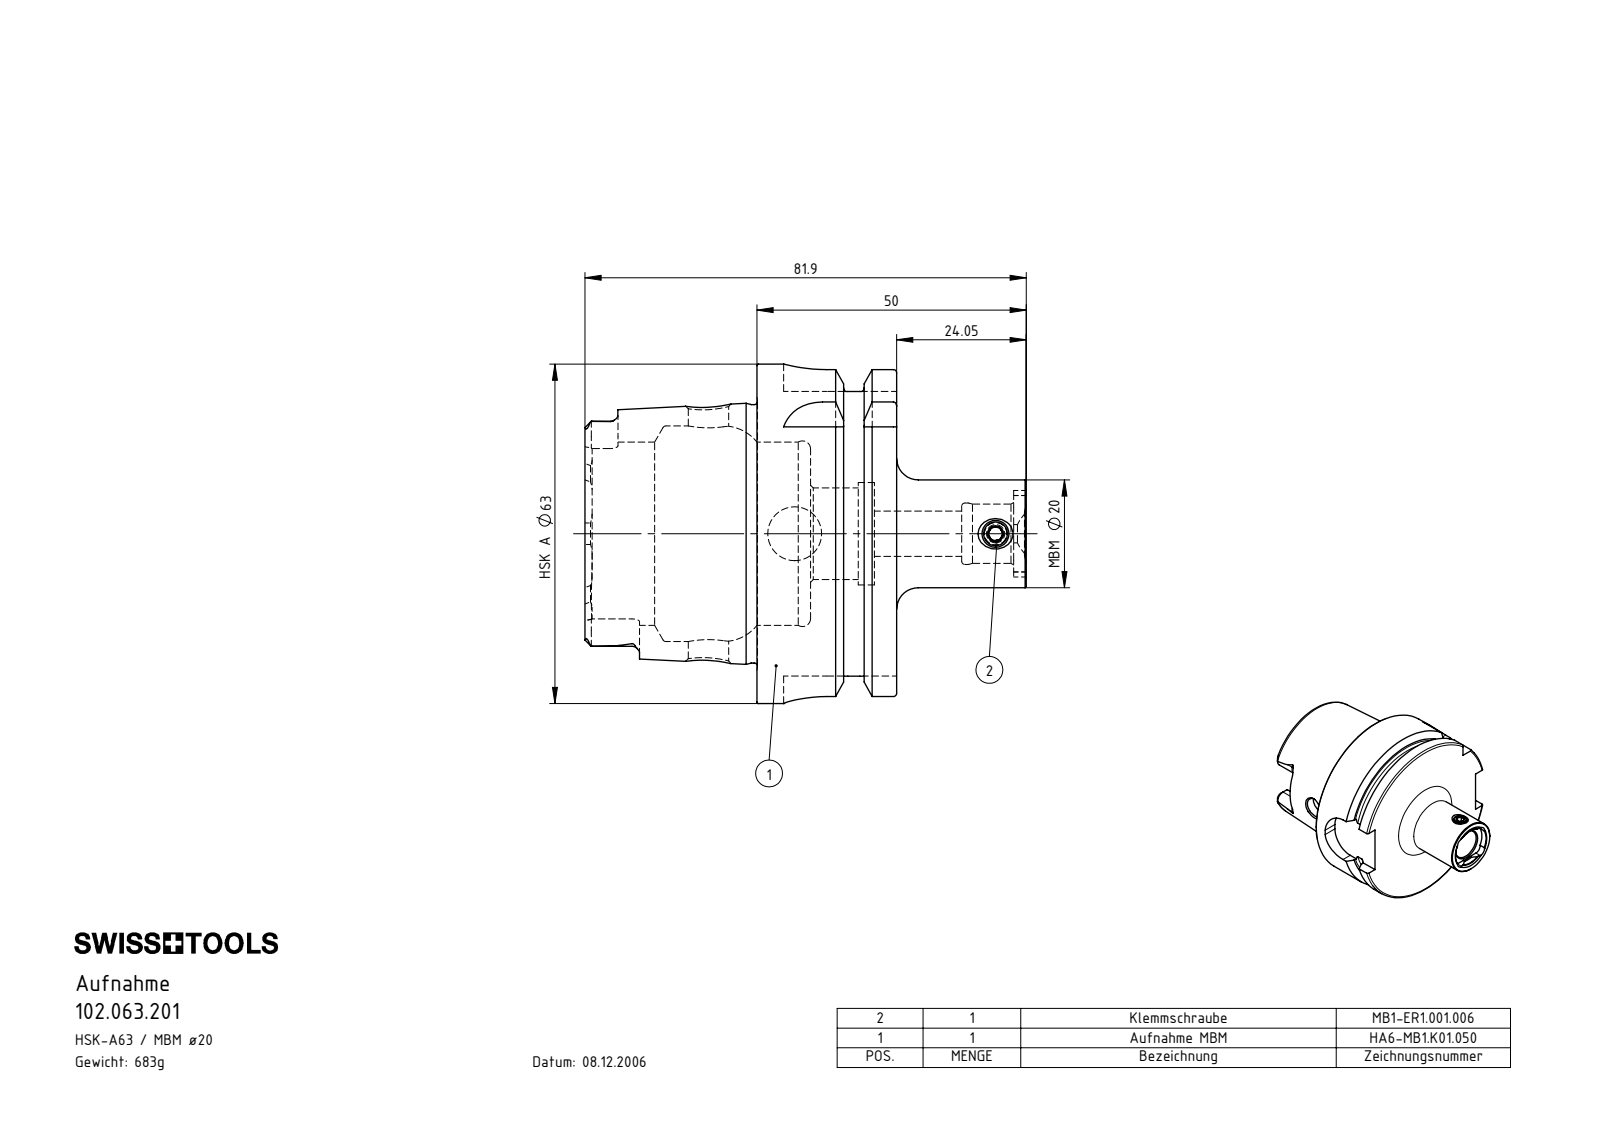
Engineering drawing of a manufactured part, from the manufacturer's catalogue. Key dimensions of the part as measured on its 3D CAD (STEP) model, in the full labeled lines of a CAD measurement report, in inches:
Part name (STEP PRODUCT): HA6.MB1.K01.050; HA6-MB1.K01.050_A_Fertigbearbeitung; MB1-ER1.001.006_A
STEP written by: SolidWorks 2012 (CONFIG_CONTROL_DESIGN)
Units: inches
Bodies: 2 solids, 228 faces (62 planar, 64 cylindrical, 102 other)
Overall size (bounding box): 3.224 × 2.48 × 2.48
Volume: 5.309 in³ · Surface area: 38.03 in²
Round holes (diameter × count): ⌀0.165 ×1, ⌀0.295 ×1, ⌀0.331 ×1, ⌀0.394 ×1, ⌀0.433 ×1, ⌀0.449 ×1, ⌀0.669 ×1, ⌀0.748 ×1, ⌀1.339 ×1, ⌀1.575 ×1
Round bosses / shafts (diameter × count): ⌀2.48 ×1, ⌀2.163 ×1, ⌀1.887 ×1, ⌀0.787 ×1, ⌀0.197 ×1
Partial cylindrical surfaces — rounded edges, fillets, slot ends (radius × count): R0.055 ×6, R0.087 ×4, R0.113 ×4, R0.315 ×4, R0.256 ×1, R0.316 ×1
Main face-to-face distances: 1.022, 0.63, 0.392, 1.256, 1.648, 2.278, 2.079, 0.858, 0.467, 2.114
Hole centre spacings: 1.469
